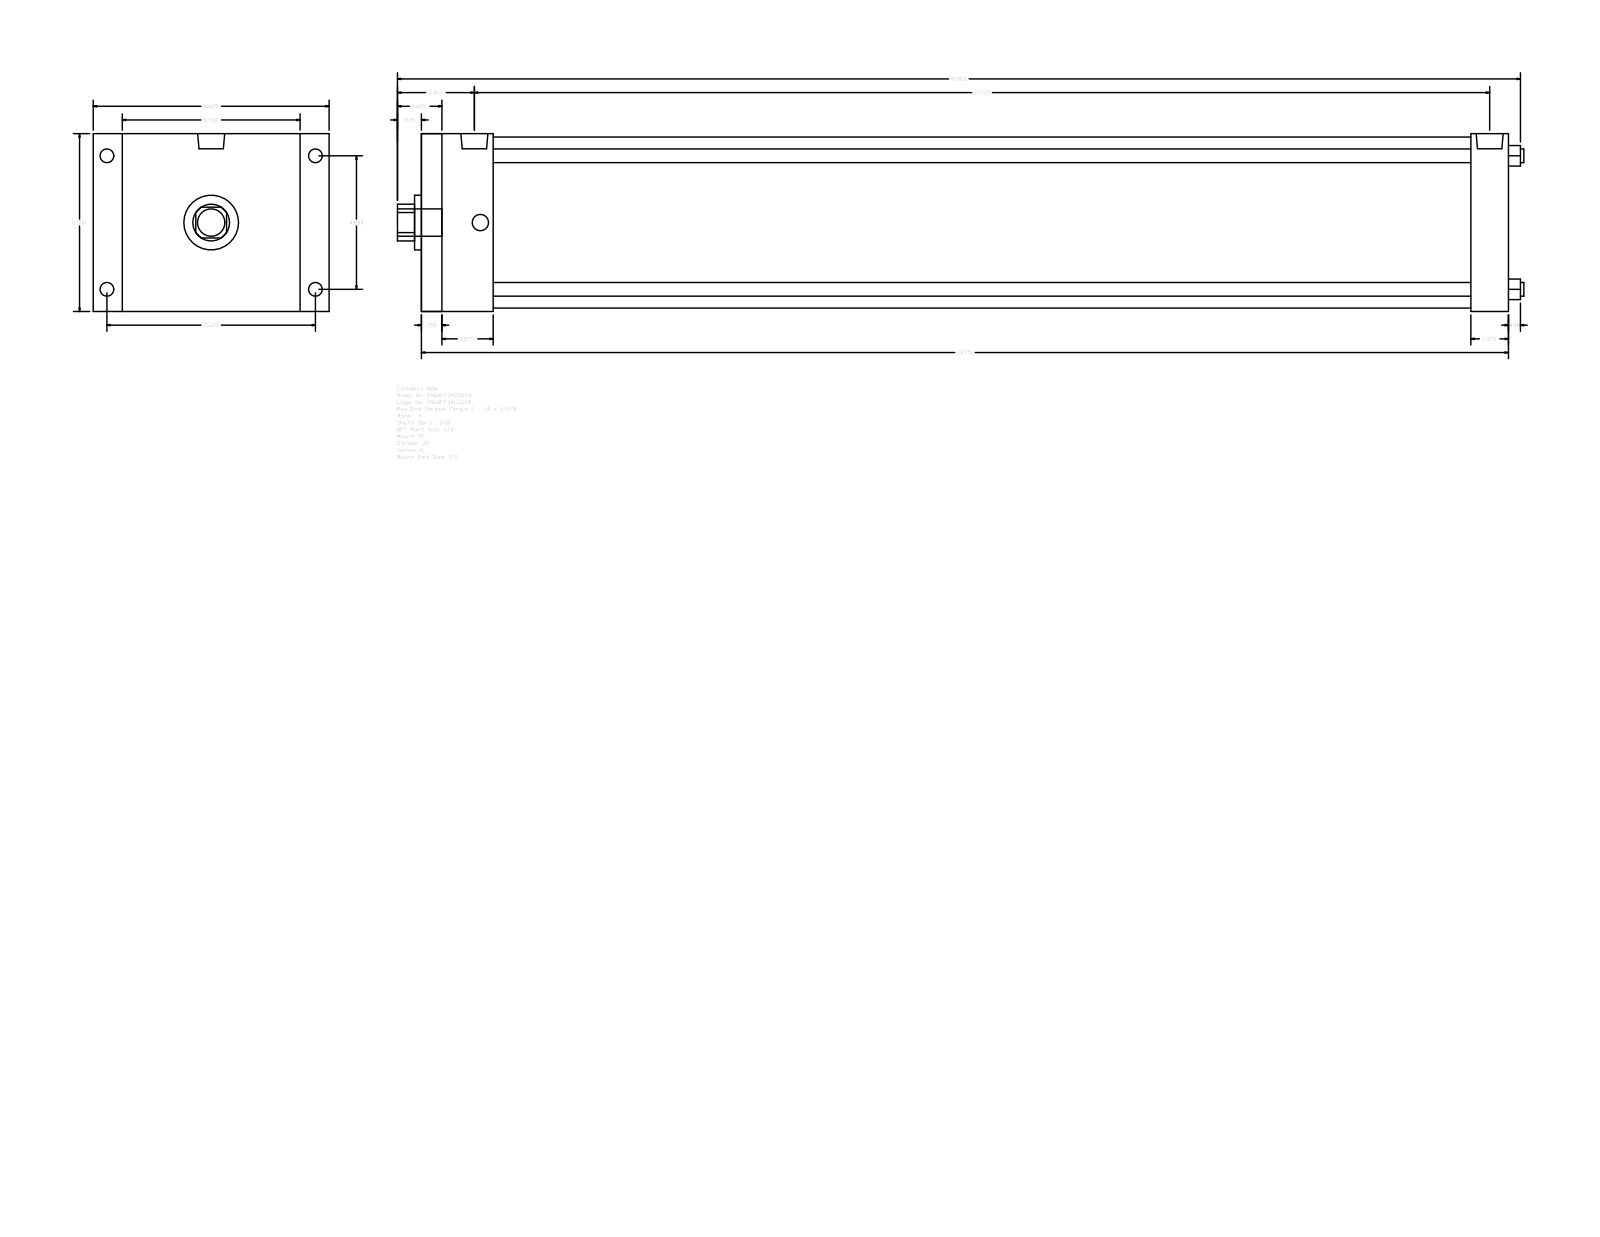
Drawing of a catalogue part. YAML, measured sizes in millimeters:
part_name: "A_FF__0600_1.375"
step_written_by: "GSSL Pune (CONFIG_CONTROL_DESIGN)"
units: millimeters
bodies: {solids: 0, faces: 92, planar: 64, cylindrical: 28, other: 0}
overall_size: [1046.16, 219.07, 165.1]
round_holes:
  - {diameter: 12.7, count: 4}
  - {diameter: 34.92, count: 1}
  - {diameter: 50.8, count: 1}
  - {diameter: 158.75, count: 1}
round_bosses_or_shafts:
  - {diameter: 15.08, count: 4}
  - {diameter: 12.7, count: 4}
  - {diameter: 25.12, count: 2}
  - {diameter: 25.4, count: 1}
partial_cylinders:
  - {radius: 17.06, count: 1}
face_to_face_distances: [165.1, 1009.65, 19.04, 990.61, 66.67, 47.63, 942.98, 974.72, 955.68, 908.05]
hole_center_spacings: [87.65, 123.96, 175.31]
